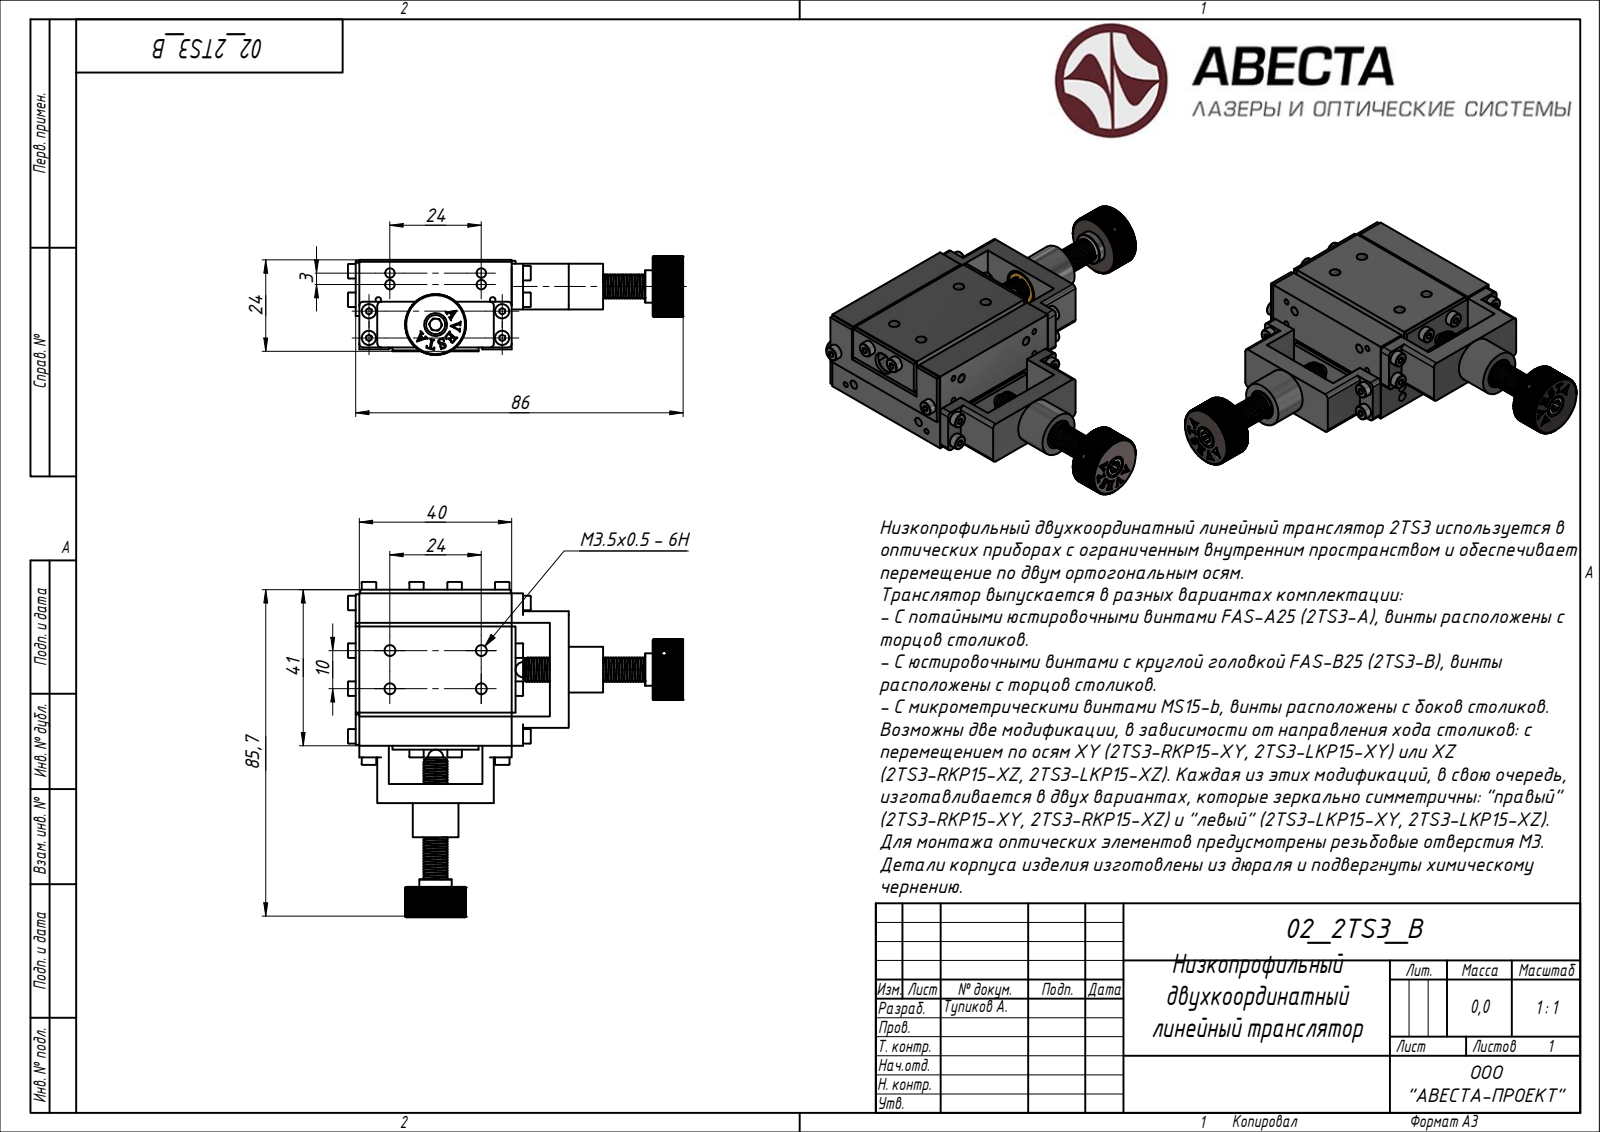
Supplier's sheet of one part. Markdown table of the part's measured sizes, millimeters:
| quantity | value |
| --- | --- |
| STEP written by | ST-DEVELOPER v15 (AUTOMOTIVE_DESIGN) |
| units | millimeters |
| bodies | 19 solids, 1223 faces (0 planar, 0 cylindrical, 1223 other) |
| overall size | 88 × 88 × 26 |
